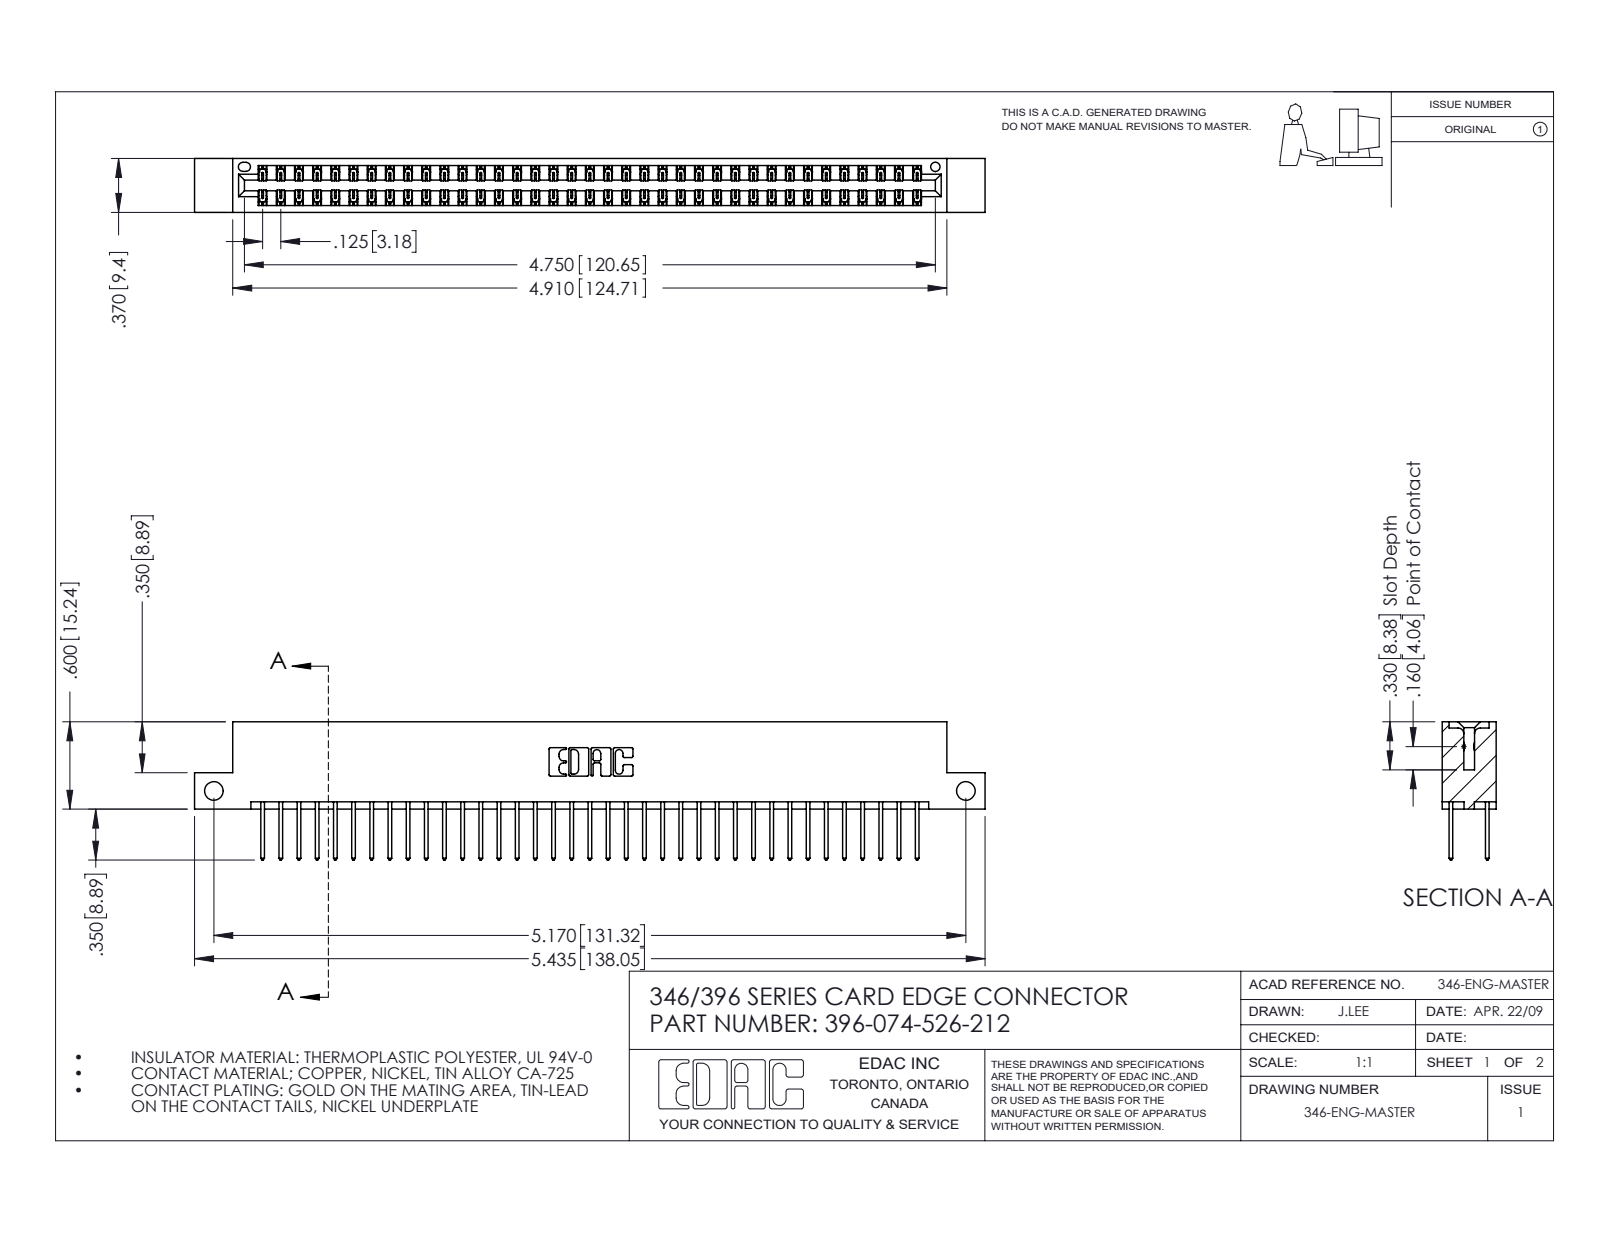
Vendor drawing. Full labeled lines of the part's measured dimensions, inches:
Part name (STEP PRODUCT): 396-074-526-212; 345-292-001_345-293-126; 346 Part_Flush Mounting Lugs - Side Mount
STEP written by: SolidWorks 2016 (CONFIG_CONTROL_DESIGN)
Units: inches
Bodies: 75 solids, 3970 faces (2666 planar, 1304 cylindrical, 0 other)
Overall size (bounding box): 5.435 × 0.95 × 0.37
Volume: 0.821 in³ · Surface area: 29.18 in²
Round holes (diameter × count): ⌀0.128 ×2, ⌀0.064 ×1
Partial cylindrical surfaces — rounded edges, fillets, slot ends (radius × count): R0.006 ×111, R0.01 ×74, R0.01 ×22, R0.007 ×6, R0.031 ×6, R0.026 ×3, R0.014 ×2, R0.022 ×2
Main face-to-face distances: 0.048, 0.322, 0.25, 0.37, 0.072, 0.298, 0.025, 0.275, 0.148, 0.222
Hole centre spacings: 5.17
